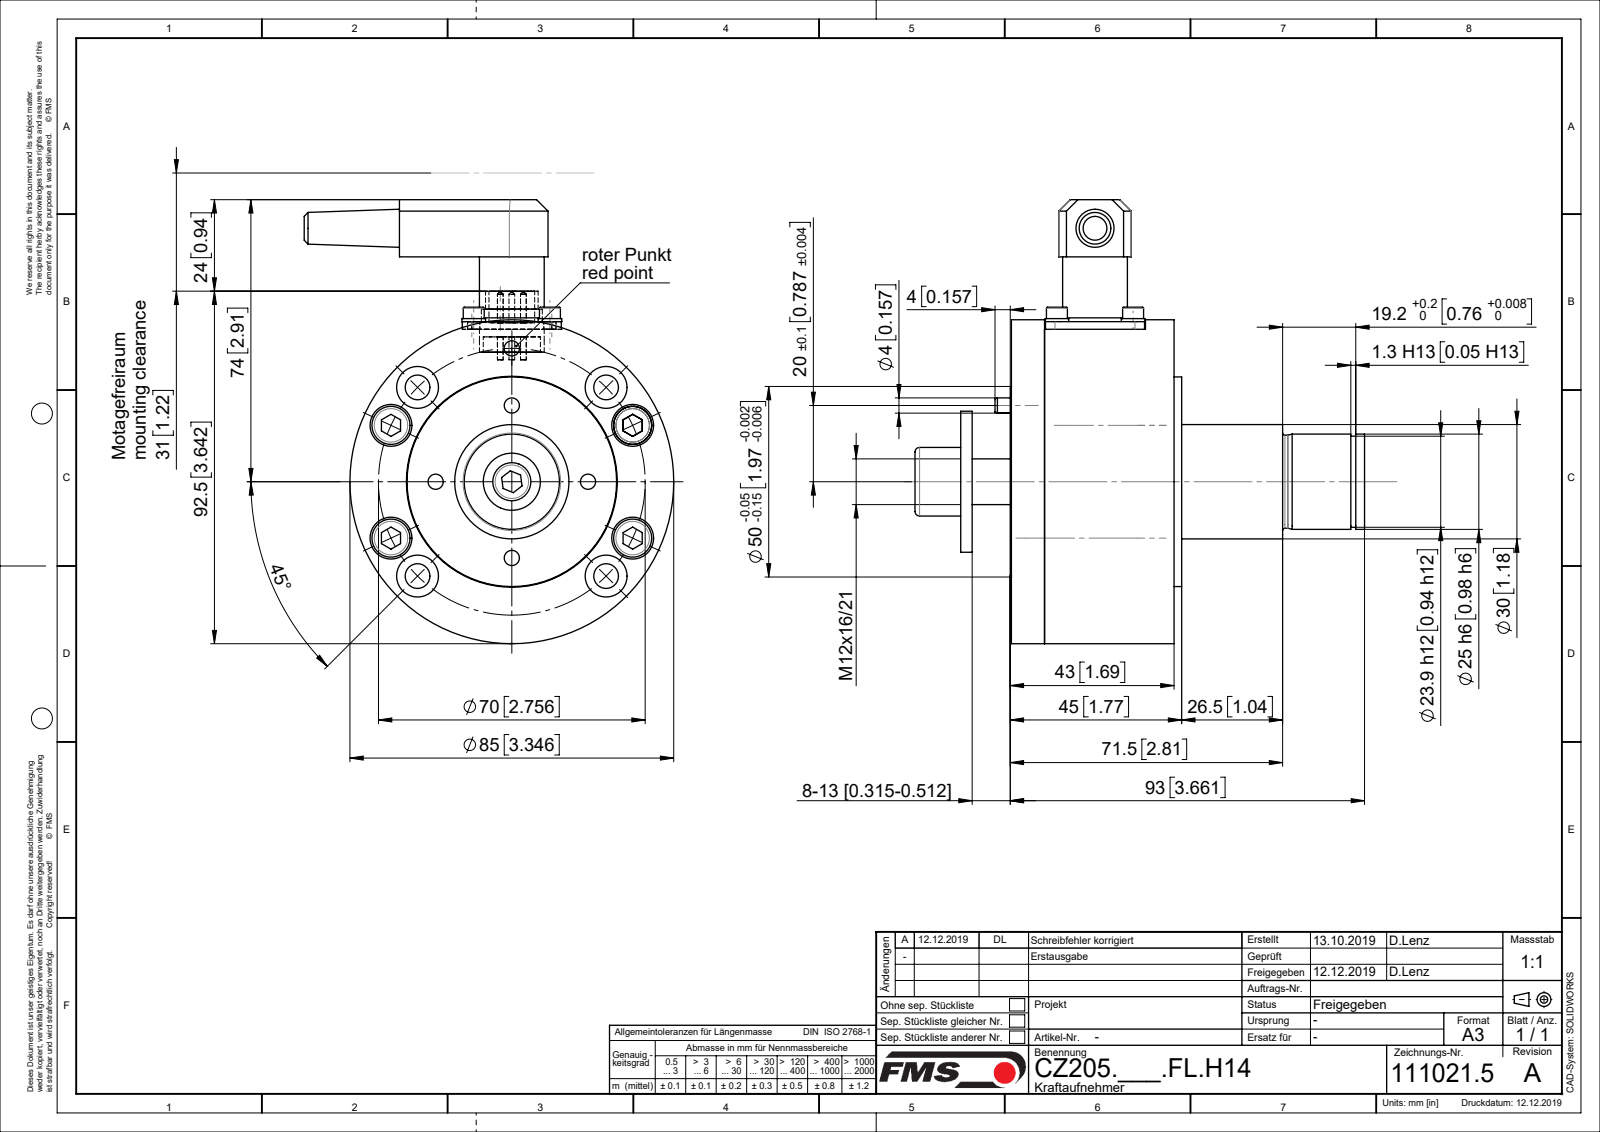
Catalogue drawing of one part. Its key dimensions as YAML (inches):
part_name: "ZEICHNUNG6; C1110215; C0709081; C0612056 (+8 more)"
step_written_by: "Mechanical Desktop 2009 (CONFIG_CONTROL_DESIGN)"
units: inches
bodies: {solids: 26, faces: 501, planar: 164, cylindrical: 250, other: 87}
overall_size: [4.685, 4.587, 3.819]
volume: 14.68
surface_area: 135.1
round_holes:
  - {diameter: 0.256, count: 8}
  - {diameter: 0.433, count: 8}
  - {diameter: 0.079, count: 5}
  - {diameter: 0.102, count: 4}
  - {diameter: 0.126, count: 4}
  - {diameter: 0.157, count: 4}
  - {diameter: 0.203, count: 4}
  - {diameter: 0.276, count: 4}
  - {diameter: 0.591, count: 2}
  - {diameter: 0.281, count: 1}
  - {diameter: 0.354, count: 1}
  - {diameter: 0.42, count: 1}
round_bosses_or_shafts:
  - {diameter: 0.059, count: 5}
  - {diameter: 0.394, count: 4}
  - {diameter: 0.244, count: 4}
  - {diameter: 0.236, count: 4}
  - {diameter: 0.217, count: 4}
  - {diameter: 0.197, count: 4}
  - {diameter: 0.118, count: 4}
  - {diameter: 3.346, count: 1}
partial_cylinders:
  - {radius: 0.098, count: 4}
  - {radius: 0.197, count: 2}
  - {radius: 0.374, count: 1}
face_to_face_distances: [1.772, 0.394, 0.343, 0.079, 1.339, 0.63, 1.681, 1.417, 1.76, 1.319]
hole_center_spacings: [0.787, 0.992, 1.378, 2.013, 1.113, 0.479, 0.557, 0.743]
